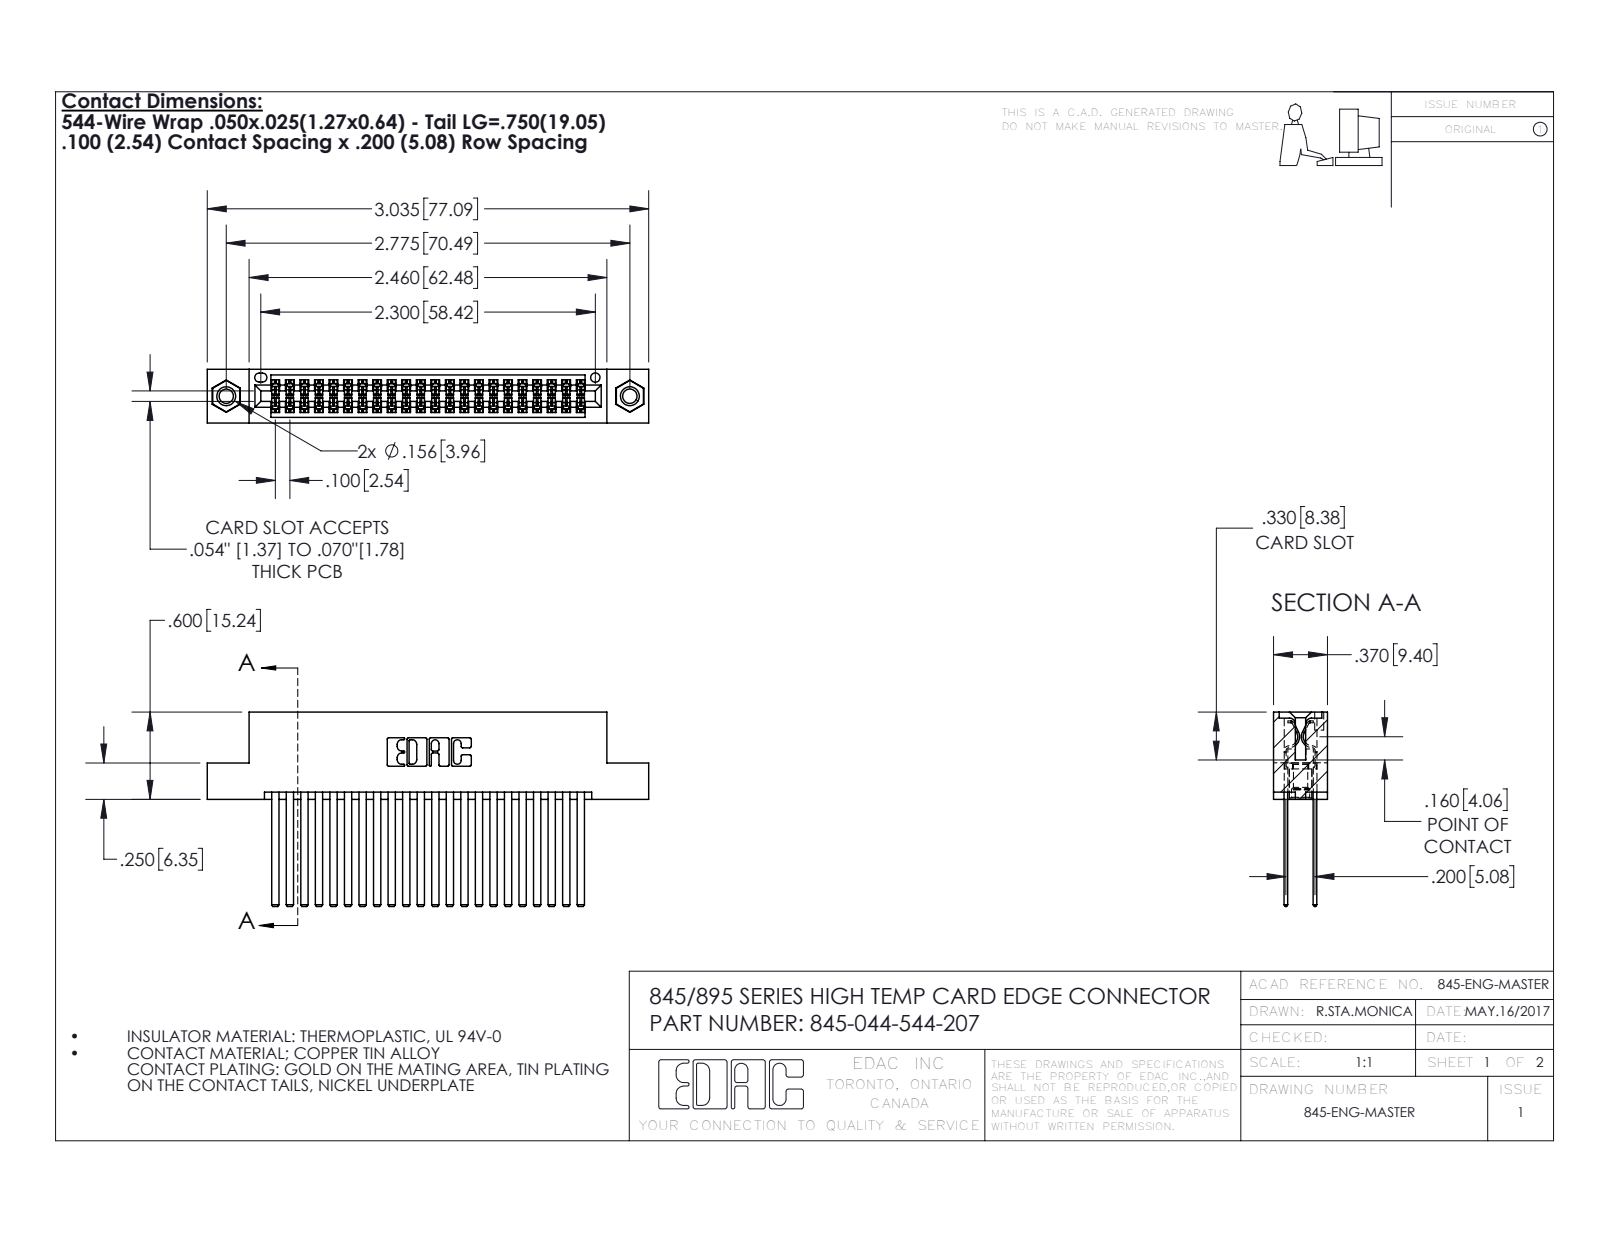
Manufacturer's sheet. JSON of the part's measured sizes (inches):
{"part_name": "345-292-001_345-293-144; 345-044-544-207; 345-250-001_345-250-005-103; 345 Part_Flush Mounting Lugs - 0.156 Dia-TI", "step_written_by": "SolidWorks 2016 (CONFIG_CONTROL_DESIGN)", "units": "inches", "bodies": {"solids": 47, "faces": 2122, "planar": 1388, "cylindrical": 718, "other": 16}, "overall_size": [3.035, 1.337, 0.37], "volume_in3": 0.482, "surface_area_in2": 20.36, "round_holes": [[0.098, 2], [0.125, 2], [0.156, 2], [0.064, 1]], "round_bosses_or_shafts": [[0.155, 2]], "partial_cylinders_radius": [[0.006, 66], [0.01, 22], [0.007, 6], [0.031, 6], [0.026, 3], [0.014, 2], [0.019, 2], [0.022, 2]], "face_to_face_distances": [0.2, 0.072, 0.298, 0.098, 0.272, 0.025, 0.225, 0.37, 0.175, 0.05], "hole_center_spacings": [0.27, 2.541, 2.775]}
